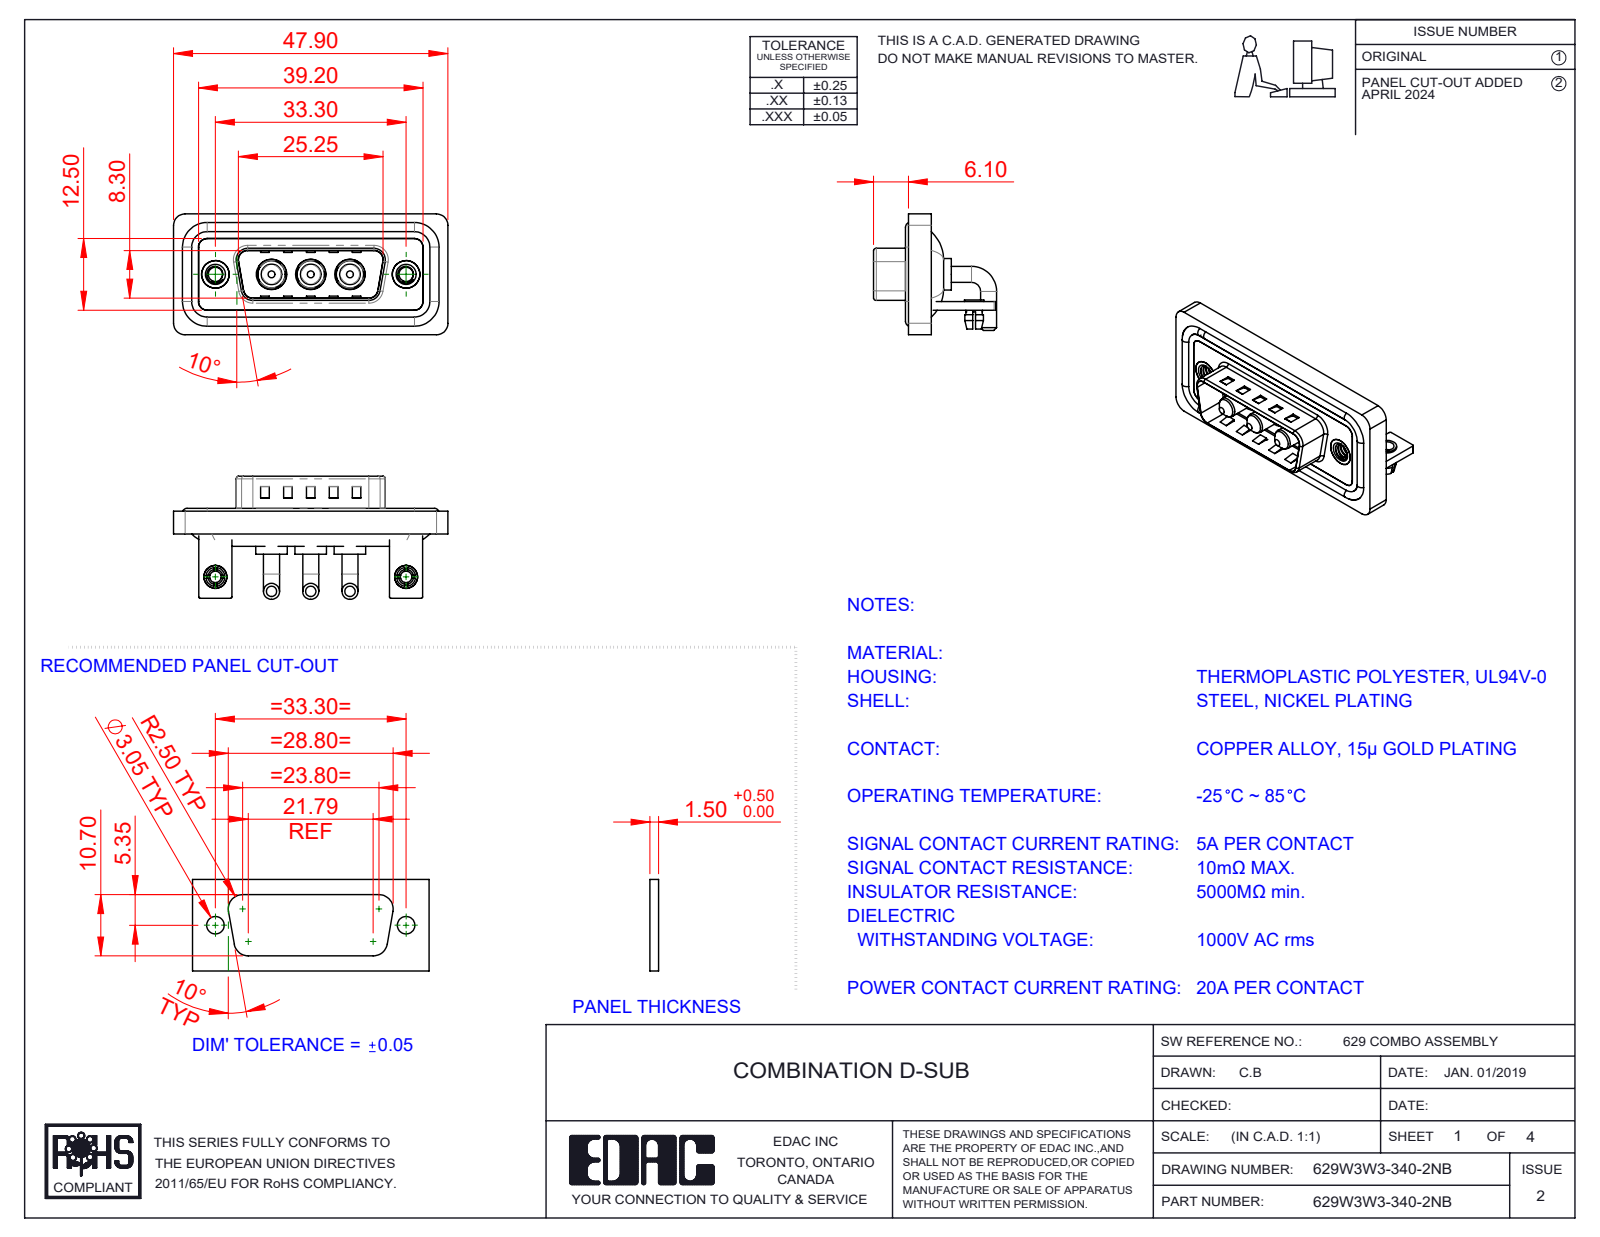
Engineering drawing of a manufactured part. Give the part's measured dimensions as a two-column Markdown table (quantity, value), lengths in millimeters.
| quantity | value |
| --- | --- |
| part name | 629W3W3-340-2NB; 629Combo Shell Front_15 Contacts; 629Combo Board Lock; 629Combo Shell Rear_15 Contacts (+5 more) |
| STEP written by | SolidWorks 2023 (CONFIG_CONTROL_DESIGN) |
| units | millimeters |
| bodies | 17 solids, 706 faces (275 planar, 297 cylindrical, 134 other) |
| overall size | 47.9 × 21.5 × 21.1 |
| volume | 6 086 mm³ |
| surface area | 9 835 mm² |
| round holes (diameter × count) | 2.5 × 4, 4.85 × 3, 5.3 × 3, 2 × 2, 3.2 × 2, 4 × 2, 4.8 × 2, 5 × 2 |
| round bosses / shafts (diameter × count) | 2.8 × 6, 1.6 × 4, 5.5 × 3, 5.2 × 3, 4.75 × 3, 3.75 × 3, 3.6 × 3, 4.9 × 2 |
| partial cylindrical surfaces (radius × count) | 2 × 21, 1.5 × 18, 0.25 × 16, 0.5 × 9, 1.6 × 8, 0.6 × 4, 0.65 × 4, 0.9 × 4 |
| main face-to-face distances | 0.4, 1.5, 0.8, 2.9, 1.1, 2.1, 3.7, 1.6, 1.2, 4.5 |
| hole center spacings | 6.85, 9.8, 16.65, 23.5, 33.3, 13.7 |
